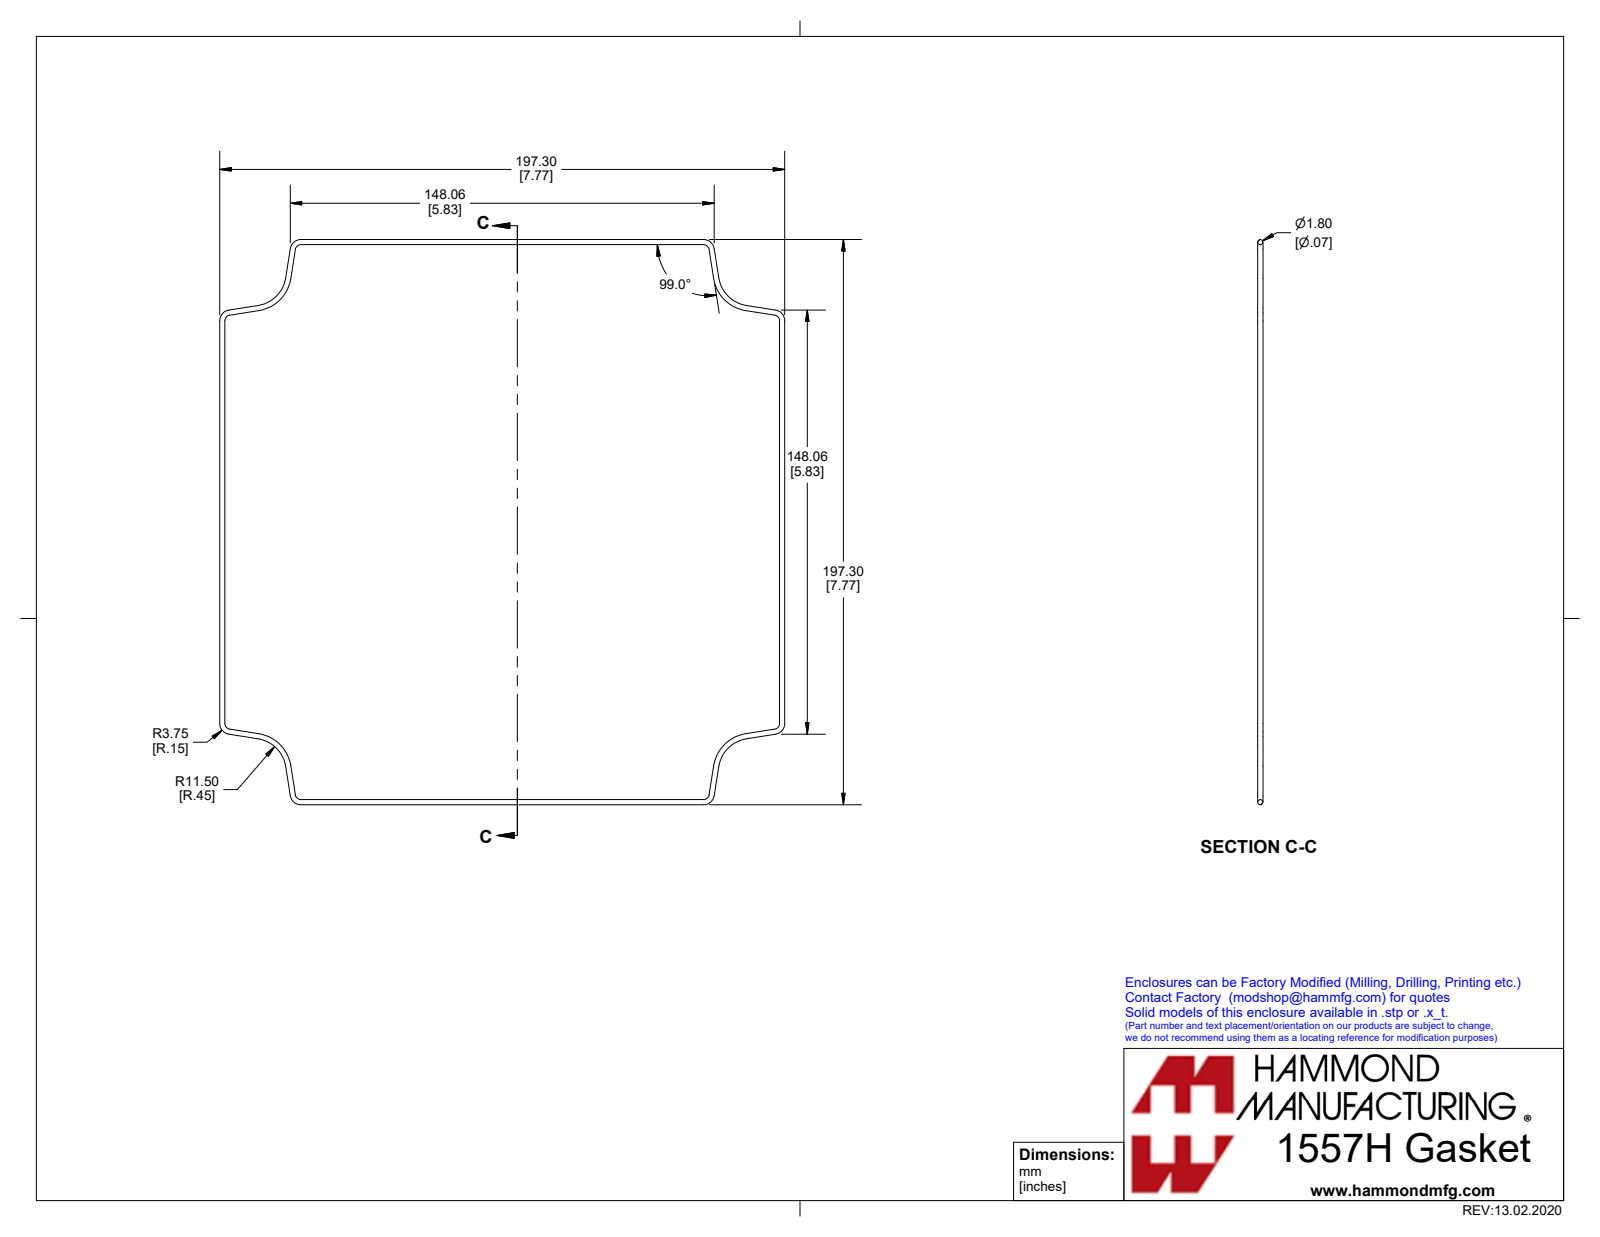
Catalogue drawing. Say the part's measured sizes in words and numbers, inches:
The part is named "1557HGASKET". Its 3-D file was written by "SolidWorks 2019 (AUTOMOTIVE_DESIGN)". It is 1 solid with 146 faces: 26 planar, 56 cylindrical and 64 other. Overall it measures 7.767 by 7.767 by 0.071 inches. Its volume is 0.122 cubic inches and its surface area 6.687 square inches. Partial cylindrical surfaces (rounded edges, fillets, slot ends): 48 of radius 0.031, 4 of radius 0.453, 4 of radius 0.524. The main face-to-face distances are 0.071, 7.697, 7.626, 7.768, 6.861, 6.791, 6.932.
